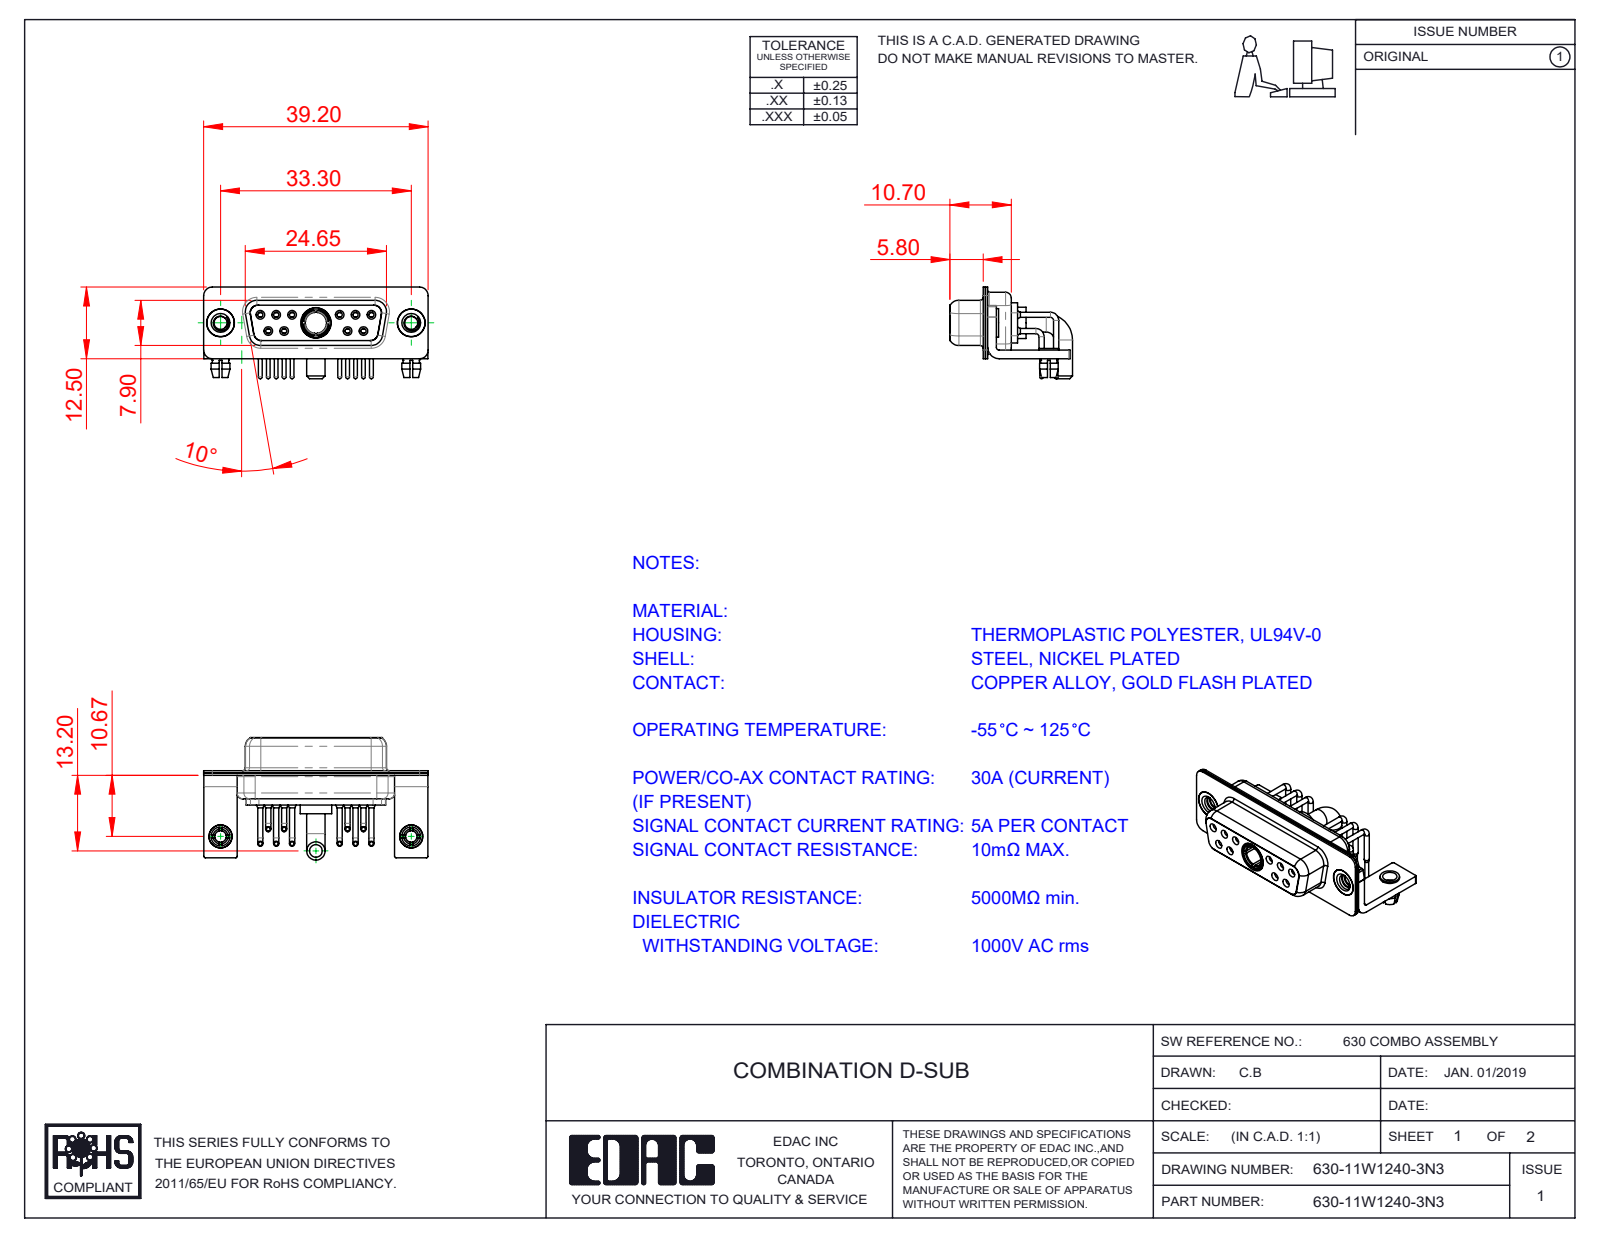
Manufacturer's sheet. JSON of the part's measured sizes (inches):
{"part_name": "630Combo Stabilizer Bracket; 630-11W1240-3N3; 630Combo Housing_11W1; 630Combo Contact Row 1 (+6 more)", "step_written_by": "SolidWorks 2020 (CONFIG_CONTROL_DESIGN)", "units": "inches", "bodies": {"solids": 21, "faces": 1019, "planar": 314, "cylindrical": 442, "other": 263}, "overall_size": [1.543, 0.843, 0.63], "volume_in3": 0.182, "surface_area_in2": 10.98, "round_holes": [[0.079, 12], [0.035, 10], [0.043, 10], [0.059, 10], [0.067, 6], [0.063, 4], [0.191, 3], [0.089, 2], [0.098, 2], [0.126, 2], [0.157, 2], [0.159, 2]], "round_bosses_or_shafts": [[0.035, 10], [0.026, 10], [0.063, 6], [0.197, 2], [0.195, 2], [0.189, 2], [0.157, 2], [0.134, 2]], "partial_cylinders_radius": [[0.01, 16], [0.059, 16], [0.079, 13], [0.053, 12], [0.063, 8], [0.02, 5], [0.024, 4], [0.026, 4]], "face_to_face_distances": [0.016, 0.031, 0.018, 0.055, 0.333, 0.059, 0.071, 0.35, 0.244, 0.091], "hole_center_spacings": [0.124, 0.109, 0.545, 0.436, 0.654, 0.198, 0.198, 0.218]}
